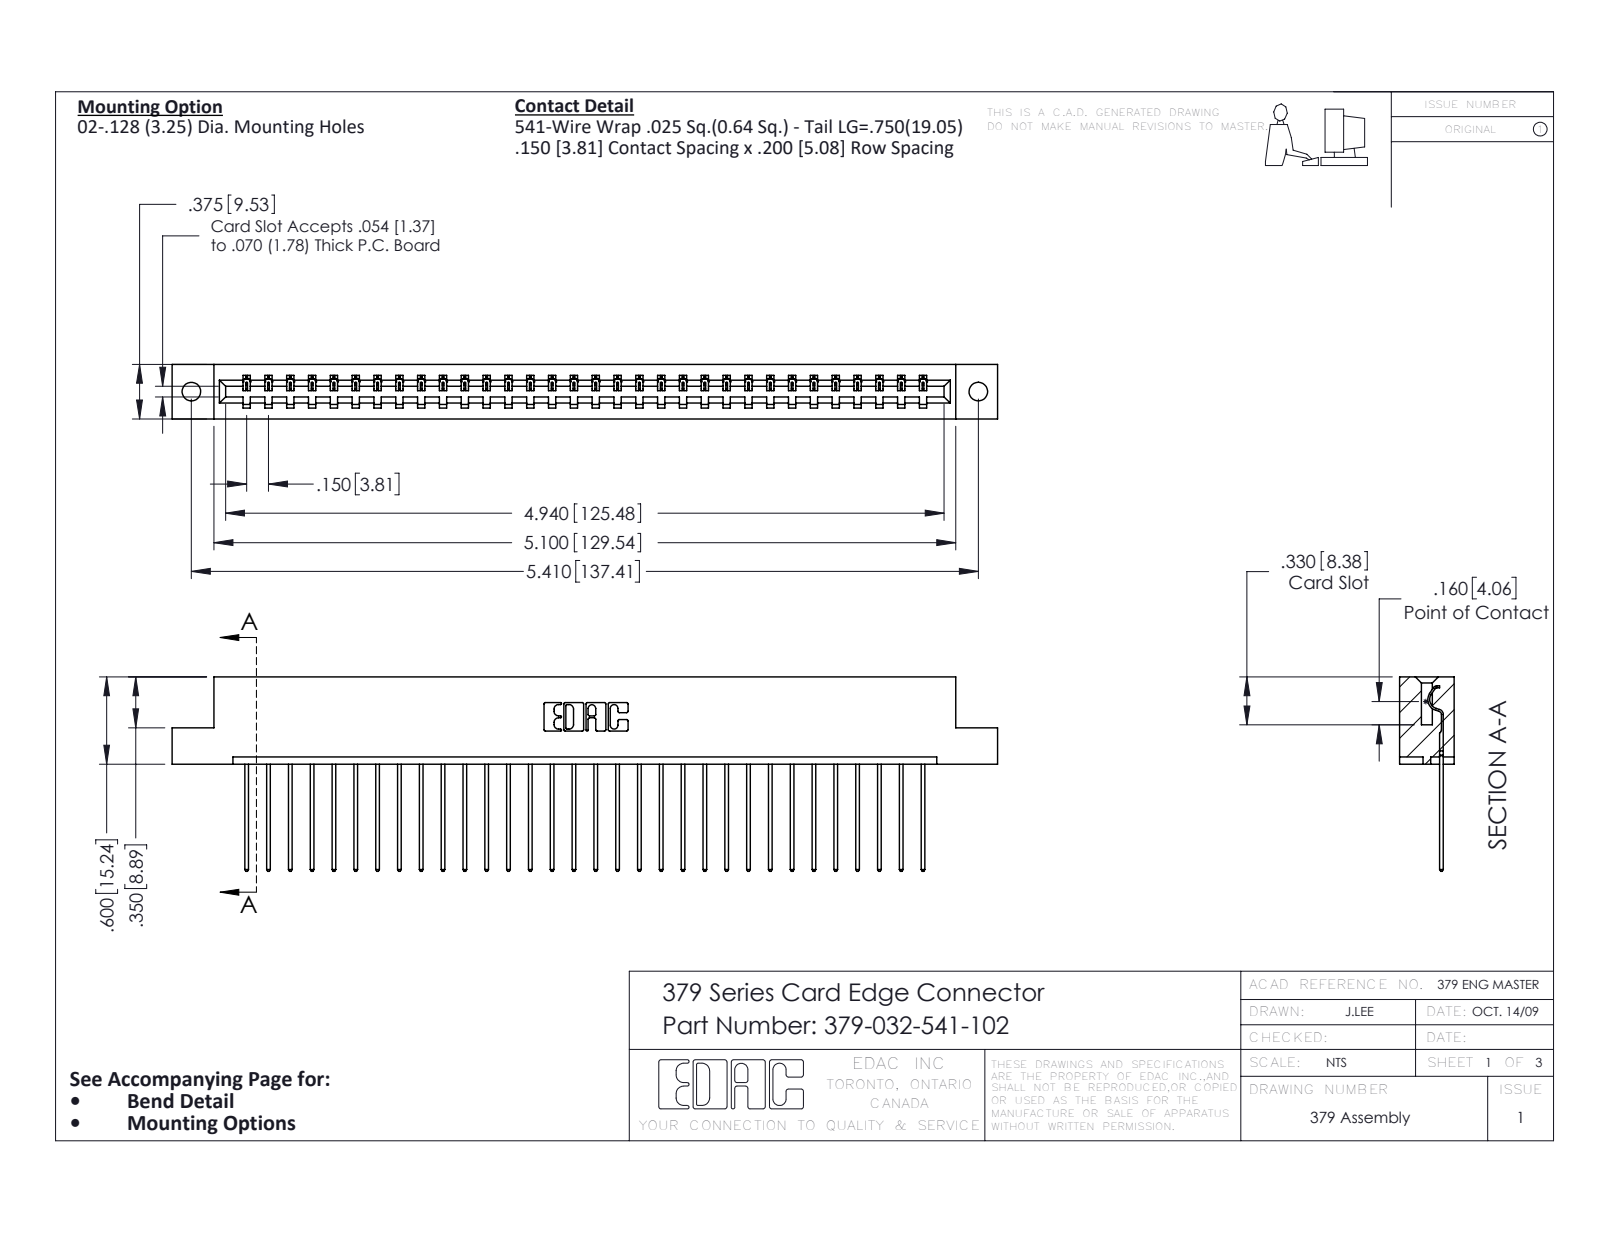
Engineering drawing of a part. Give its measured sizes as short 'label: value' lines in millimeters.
name: 379-032-541-102; 345-292-001_345-293-141; 379 Part_Flush - .128 Dia
written by: SolidWorks 2016 (CONFIG_CONTROL_DESIGN)
unit: mm
bodies: 33 solids, 1970 faces (1414 planar, 556 cylindrical, 0 other)
size: 144.1 × 34 × 9.5
volume: 15 100 mm³; area: 15 770 mm²
holes: 2× ⌀3.3
rounds: 64× R0.2, 64× R0.3, 22× R0.3, 6× R0.2, 6× R0.8, 3× R0.7, 1× R0.4, 1× R0.6
face distances: 7.6, 1.9, 9.5, 5.7, 7, 2.5, 0.6, 5.1, 15.2, 14
hole spacings: 137.4
